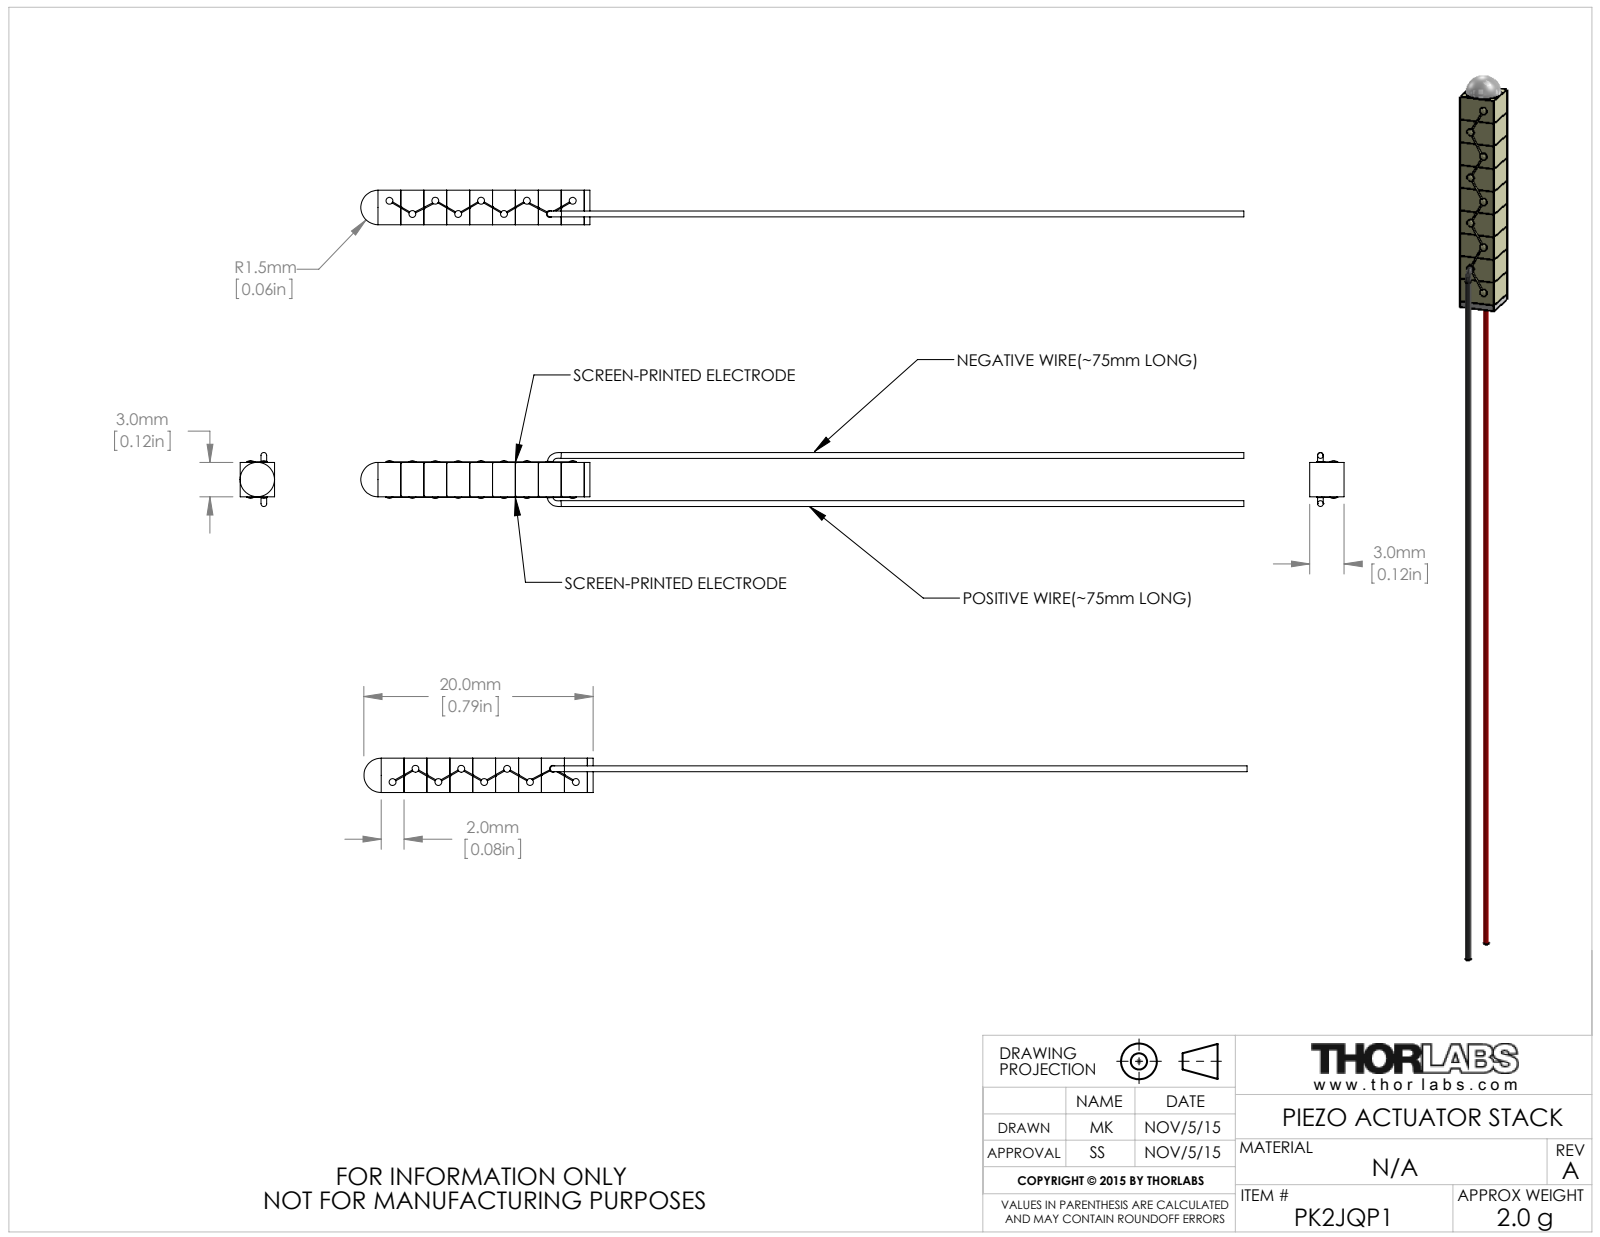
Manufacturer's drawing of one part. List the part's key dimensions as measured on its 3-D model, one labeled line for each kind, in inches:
Part name (STEP PRODUCT): CTN003186
STEP written by: SolidWorks 2014 (AUTOMOTIVE_DESIGN)
Units: inches
Bodies: 2 solids, 202 faces (79 planar, 83 cylindrical, 40 other)
Overall size (bounding box): 3.035 × 0.186 × 0.118
Volume: 0.012 in³ · Surface area: 0.938 in²
Round bosses / shafts (diameter × count): ⌀0.024 ×9
Main face-to-face distances: 0.079, 0.157, 0.118, 0.236, 0.315, 0.394, 0.472, 0.551, 0.63, 0.02
